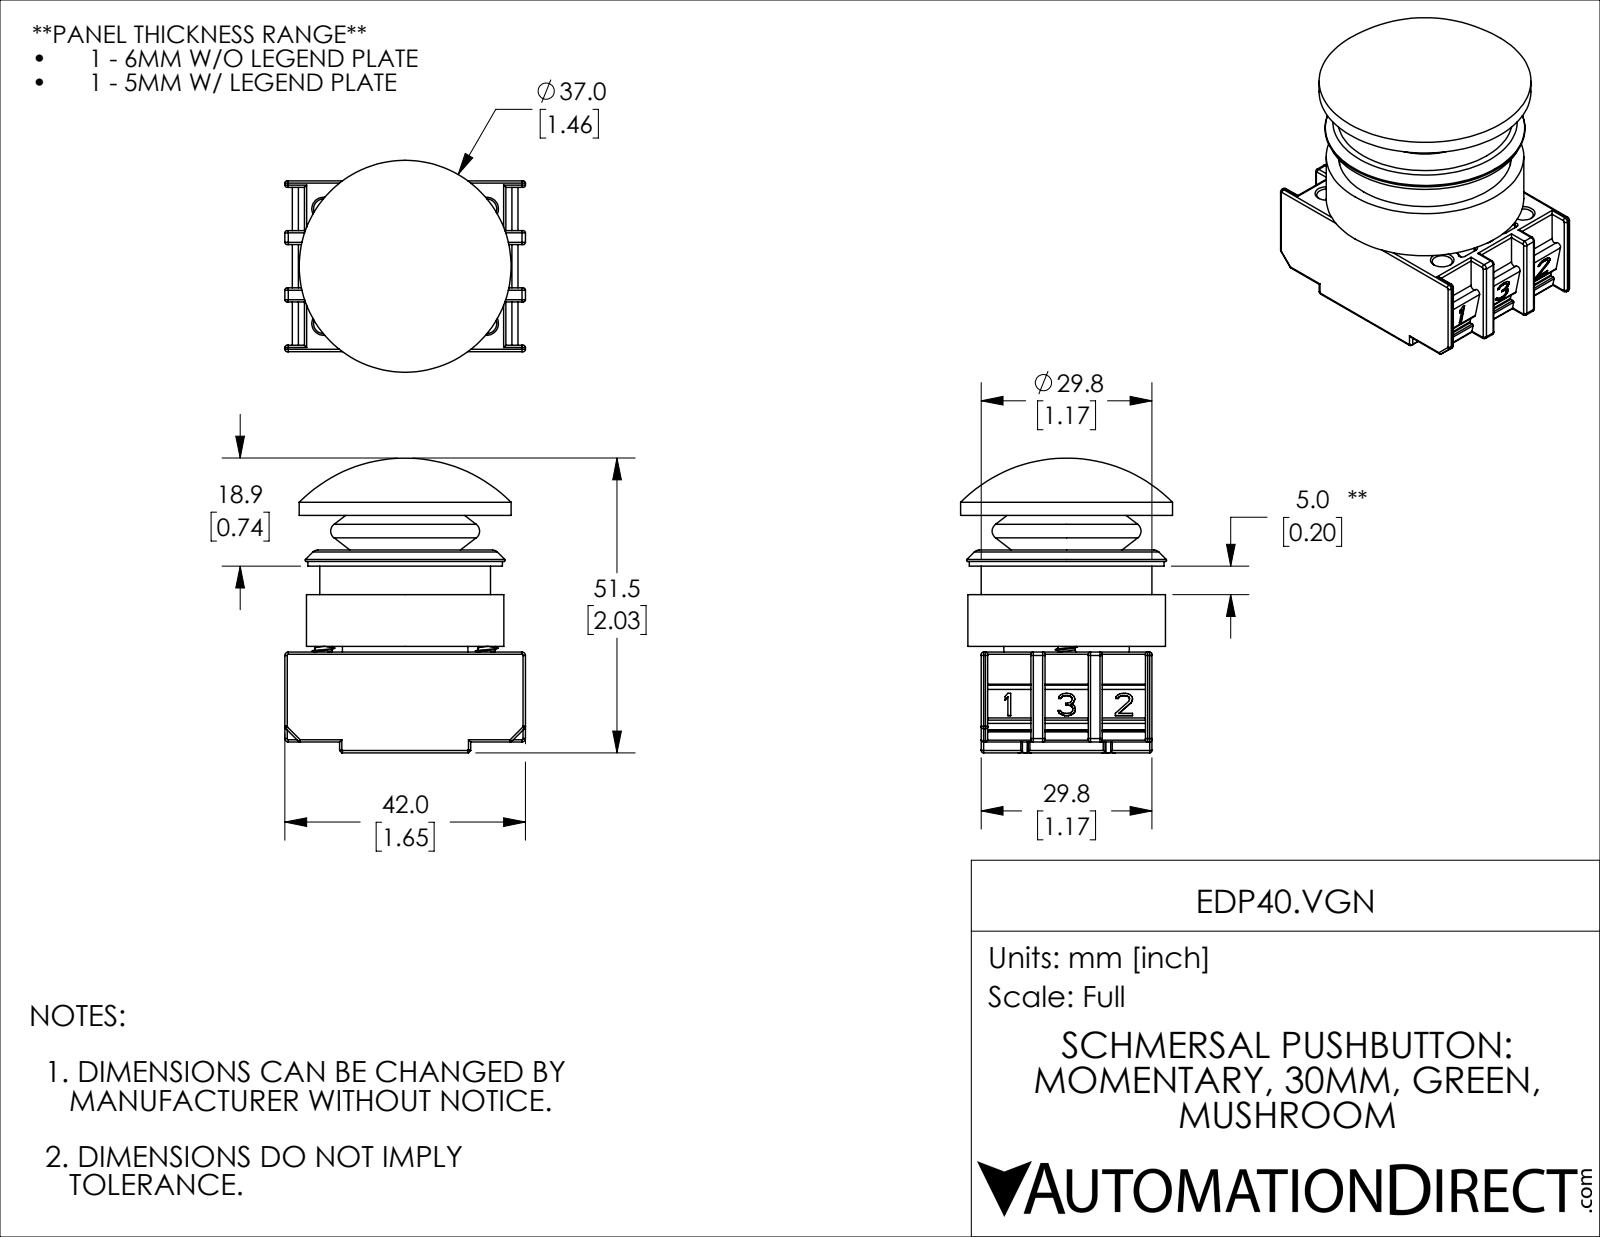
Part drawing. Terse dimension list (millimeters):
name: EDP40.VGN
written by: SolidWorks 2019 (CONFIG_CONTROL_DESIGN)
unit: mm
bodies: 5 solids, 1490 faces (538 planar, 503 cylindrical, 449 other)
size: 51.45 × 42 × 37
volume: 32 755 mm³; area: 23 609 mm²
holes: 6× ⌀3.5, 6× ⌀5.15, 1× ⌀8.25, 1× ⌀12.15, 1× ⌀18.8, 1× ⌀19.5, 1× ⌀24.1, 1× ⌀24.2, 1× ⌀26, 1× ⌀30.2, 1× ⌀32
bosses: 2× ⌀4.8, 2× ⌀2.93, 1× ⌀37, 1× ⌀34.5, 1× ⌀34, 1× ⌀29.8, 1× ⌀25.5, 1× ⌀24
rounds: 112× R0.4, 48× R0.3, 28× R0.2, 8× R0.6, 6× R0.5, 6× R0.8, 2× R0.1, 2× R0.6
face distances: 18.6, 29.8, 1, 1.9, 16.8, 17.6, 35.4, 17.8, 20.95, 10
hole spacings: 10, 17.41, 30.2, 28.5, 14.25, 20, 34.82
